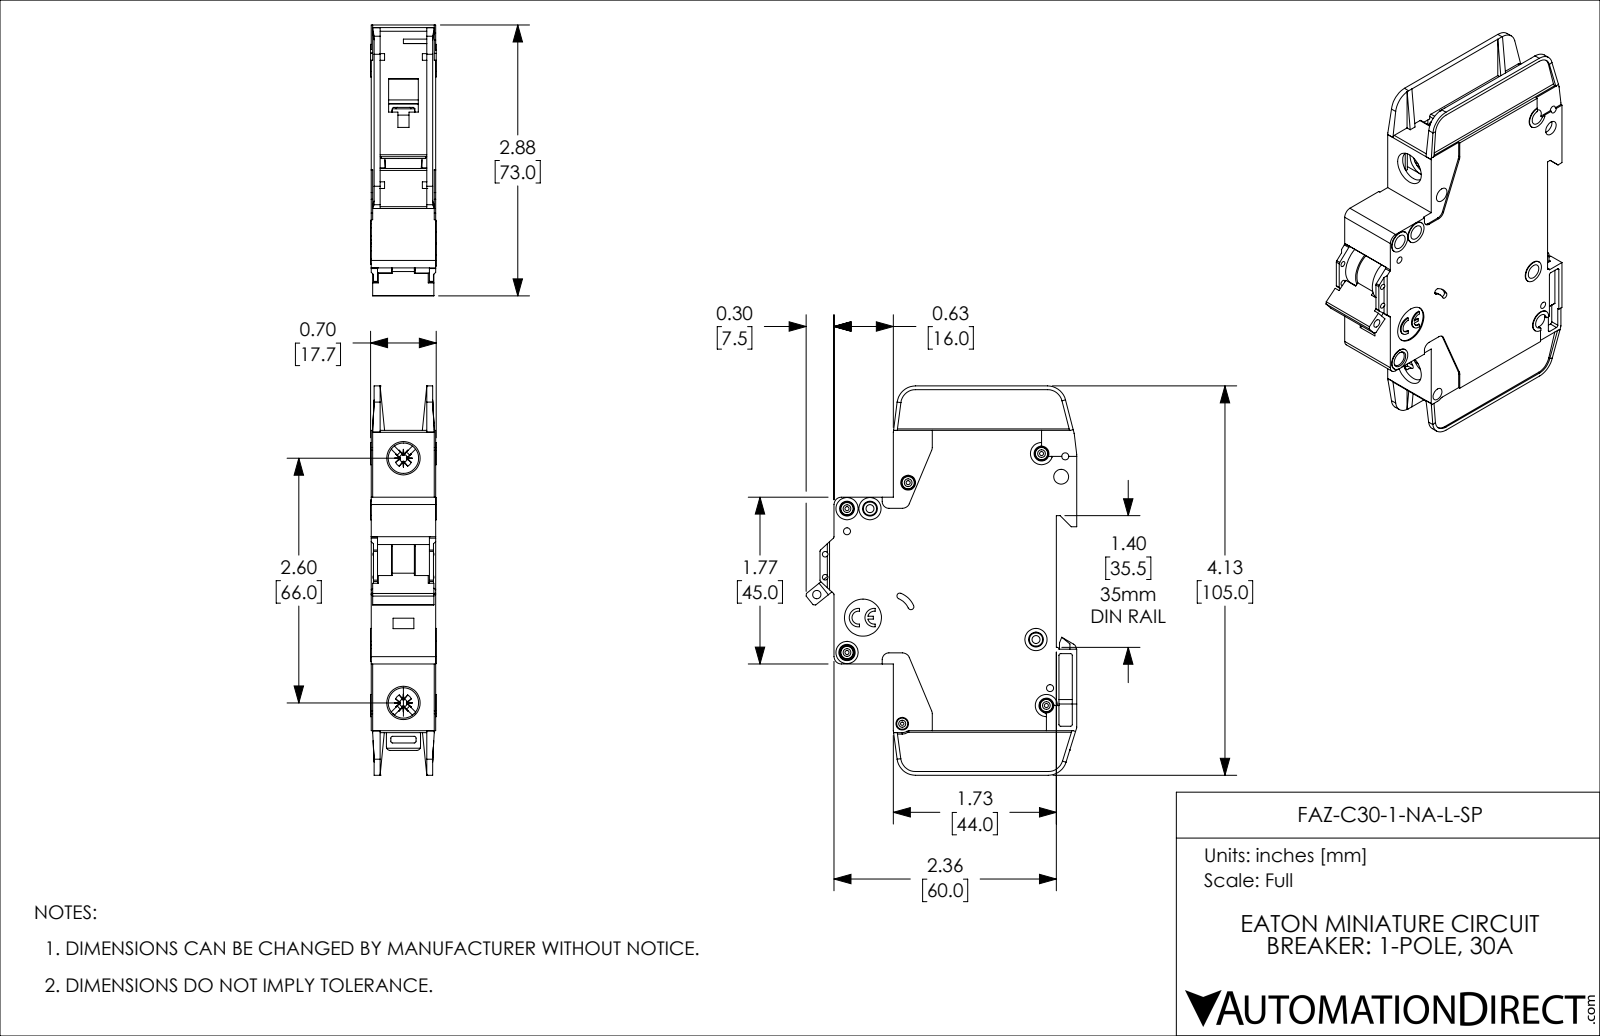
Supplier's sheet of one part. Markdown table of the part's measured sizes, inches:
| quantity | value |
| --- | --- |
| part name | FAZ-C30-1-NA-L-SP |
| STEP written by | SolidWorks 2019 (AUTOMOTIVE_DESIGN) |
| units | inches |
| bodies | 1 solid, 1127 faces (671 planar, 357 cylindrical, 99 other) |
| overall size | 4.134 × 2.876 × 0.697 |
| volume | 4.682 in³ |
| surface area | 41.01 in² |
| round holes (diameter × count) | 0.157 × 8, 0.043 × 5, 0.075 × 4, 0.059 × 2, 0.085 × 2, 0.323 × 2, 0.035 × 1, 0.089 × 1, 0.098 × 1, 0.134 × 1, 0.394 × 1 |
| round bosses / shafts (diameter × count) | 0.13 × 5, 0.236 × 4, 0.118 × 2, 0.098 × 1 |
| partial cylindrical surfaces (radius × count) | 0.02 × 42, 0.016 × 10, 0.039 × 10, 0.079 × 8, 0.197 × 5, 0.008 × 4, 0.026 × 4, 0.043 × 4 |
| main face-to-face distances | 0.047, 0.685, 0.591, 0.638, 0.094, 0.543, 0.016, 0.031, 0.496, 0.575 |
| hole center spacings | 0.244, 0.537, 0.87, 0.189, 0.199, 0.204, 0.221, 0.24 |
